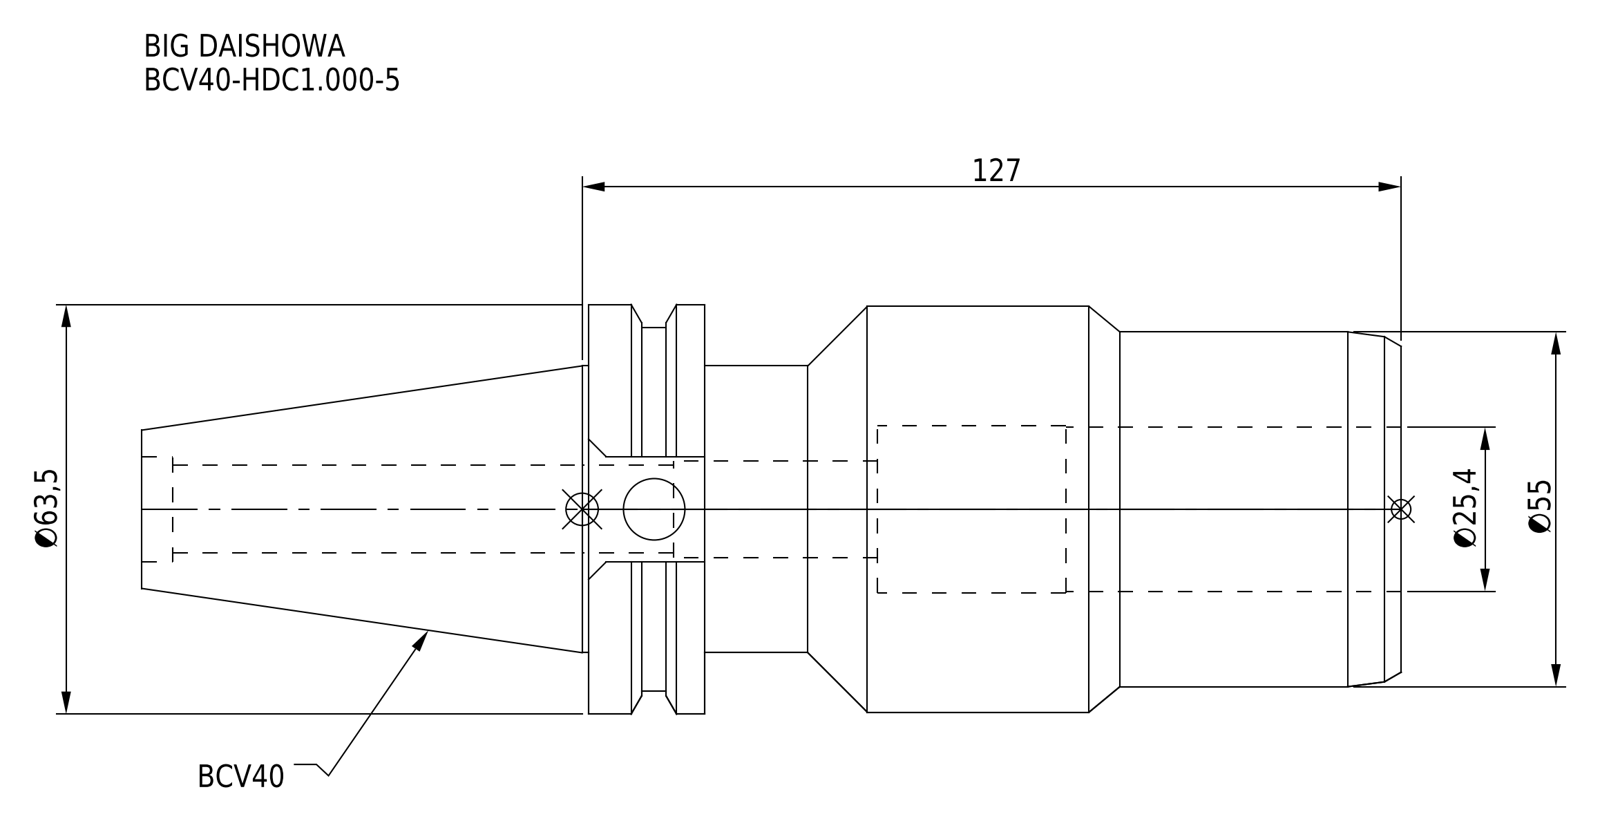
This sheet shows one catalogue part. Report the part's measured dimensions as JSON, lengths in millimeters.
{"part_name": "BCV40-HDC1_000-5", "step_written_by": "CREO PARAMETRIC BY PTC INC, 2016380 (AUTOMOTIVE_DESIGN)", "units": "millimeters", "bodies": {"solids": 1, "faces": 65, "planar": 23, "cylindrical": 28, "other": 14}, "overall_size": [195.25, 63.5, 62.9], "volume_mm3": 325527, "surface_area_mm2": 48695, "round_holes": [[9.53, 1], [13.6, 1], [15, 1], [16.32, 1], [25.4, 1], [25.9, 1]], "round_bosses_or_shafts": [[63.5, 1], [62.9, 1], [56.36, 1], [55, 1], [44.45, 1]], "face_to_face_distances": [107.95, 126, 18.05, 81.2, 26.75, 44.8, 195.25, 114.05, 87.3, 69.25]}
